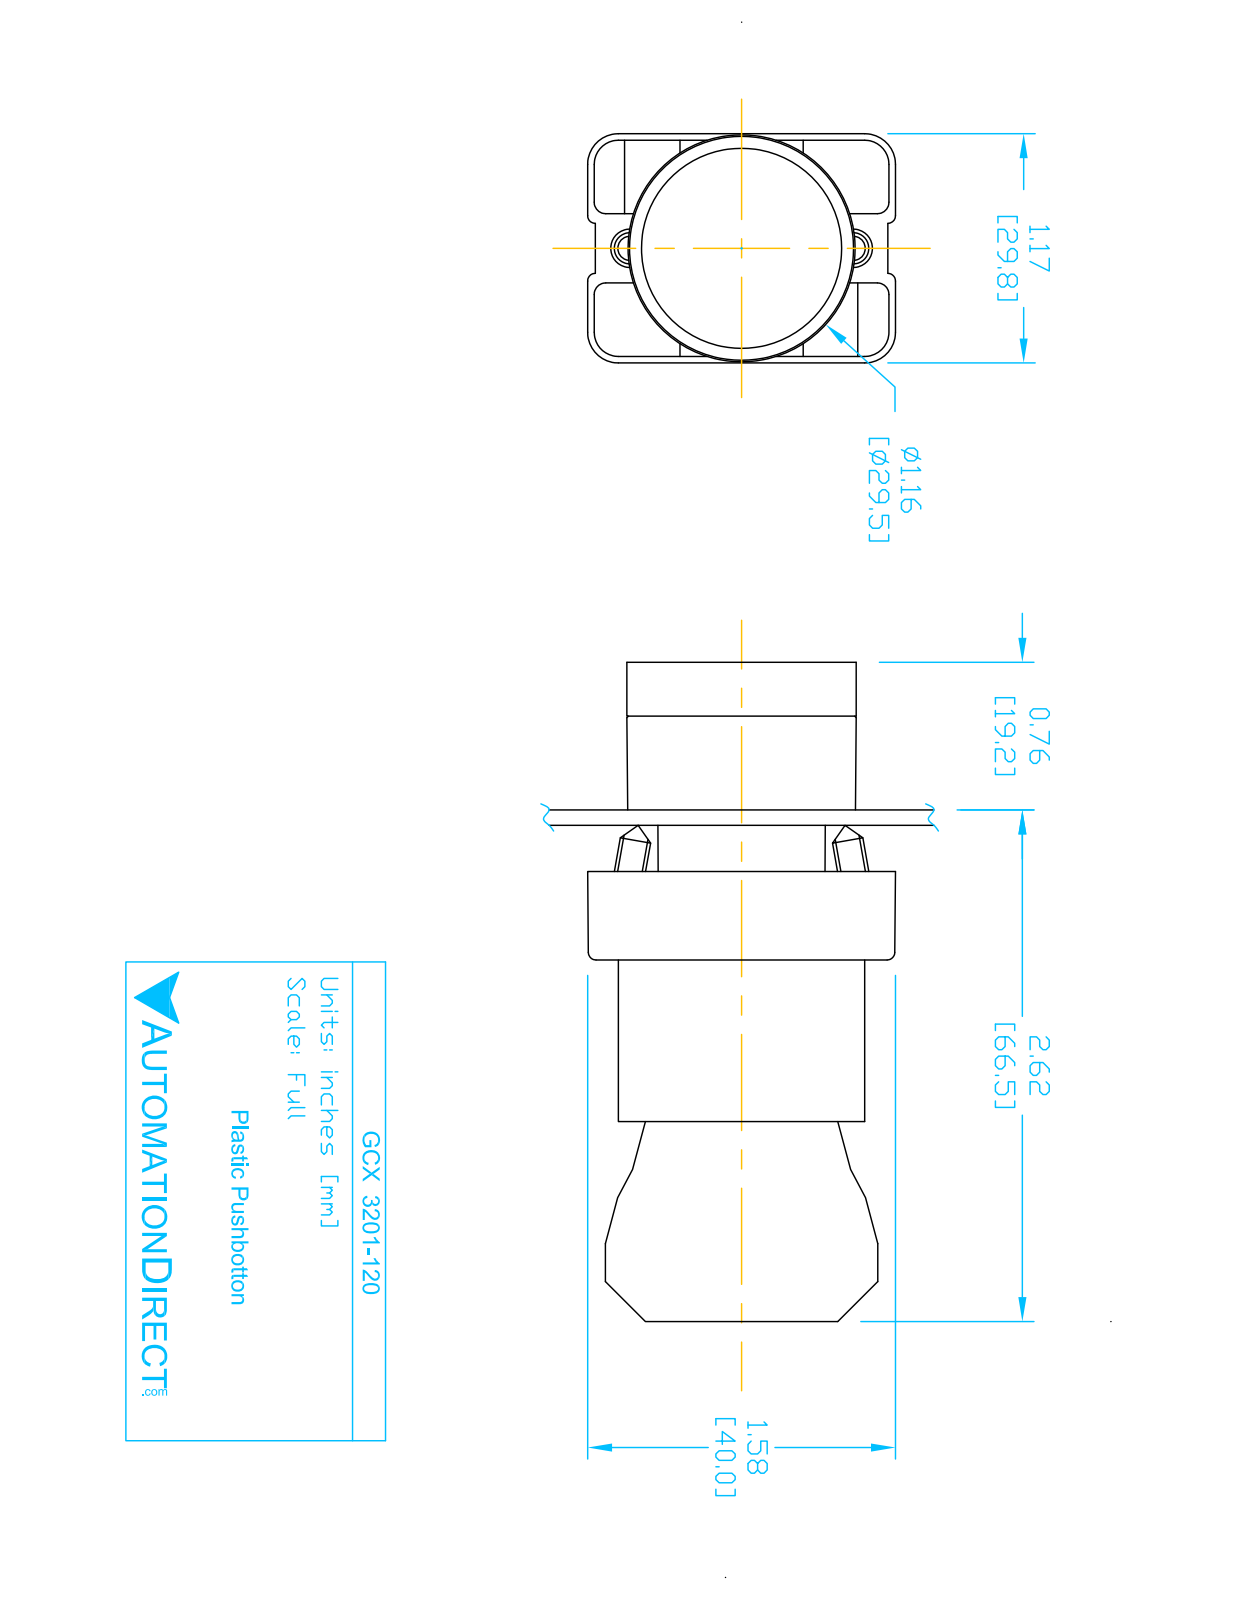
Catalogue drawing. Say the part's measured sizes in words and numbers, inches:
The part is named "GCX3201-120; ECX3029-2; ecx1030; GCX3201 OPERATOR (+1 more)". Its 3-D file was written by "SolidWorks 2016 (AUTOMOTIVE_DESIGN)". It is 8 solids with 431 faces: 252 planar, 148 cylindrical and 31 other. Overall it measures 3.319 by 1.581 by 1.177 inches. Its volume is 2.794 cubic inches and its surface area 38.77 square inches. Round holes: 2 of diameter 0.079, 2 of diameter 0.124, 2 of diameter 0.13, 1 of diameter 0.087, 1 of diameter 0.197, 1 of diameter 0.469, 1 of diameter 0.878, 1 of diameter 0.888, 1 of diameter 1.024. Round bosses or shafts: 4 of diameter 0.157, 1 of diameter 1.175, 1 of diameter 1.004, 1 of diameter 0.945, 1 of diameter 0.856, 1 of diameter 0.78, 1 of diameter 0.504. Partial cylindrical surfaces (rounded edges, fillets, slot ends): 24 of radius 0.059, 12 of radius 0.041, 12 of radius 0.124, 12 of radius 0.157, 8 of radius 0.039, 2 of radius 0.128, 1 of radius 0.02, 1 of radius 0.063. The main face-to-face distances are 0.827, 0.579, 2.02, 1.193, 1.171, 0.276, 2.295, 1.469, 0.031, 0.033. The hole center spacings are 0.236, 0.544, 0.472, 0.49.
